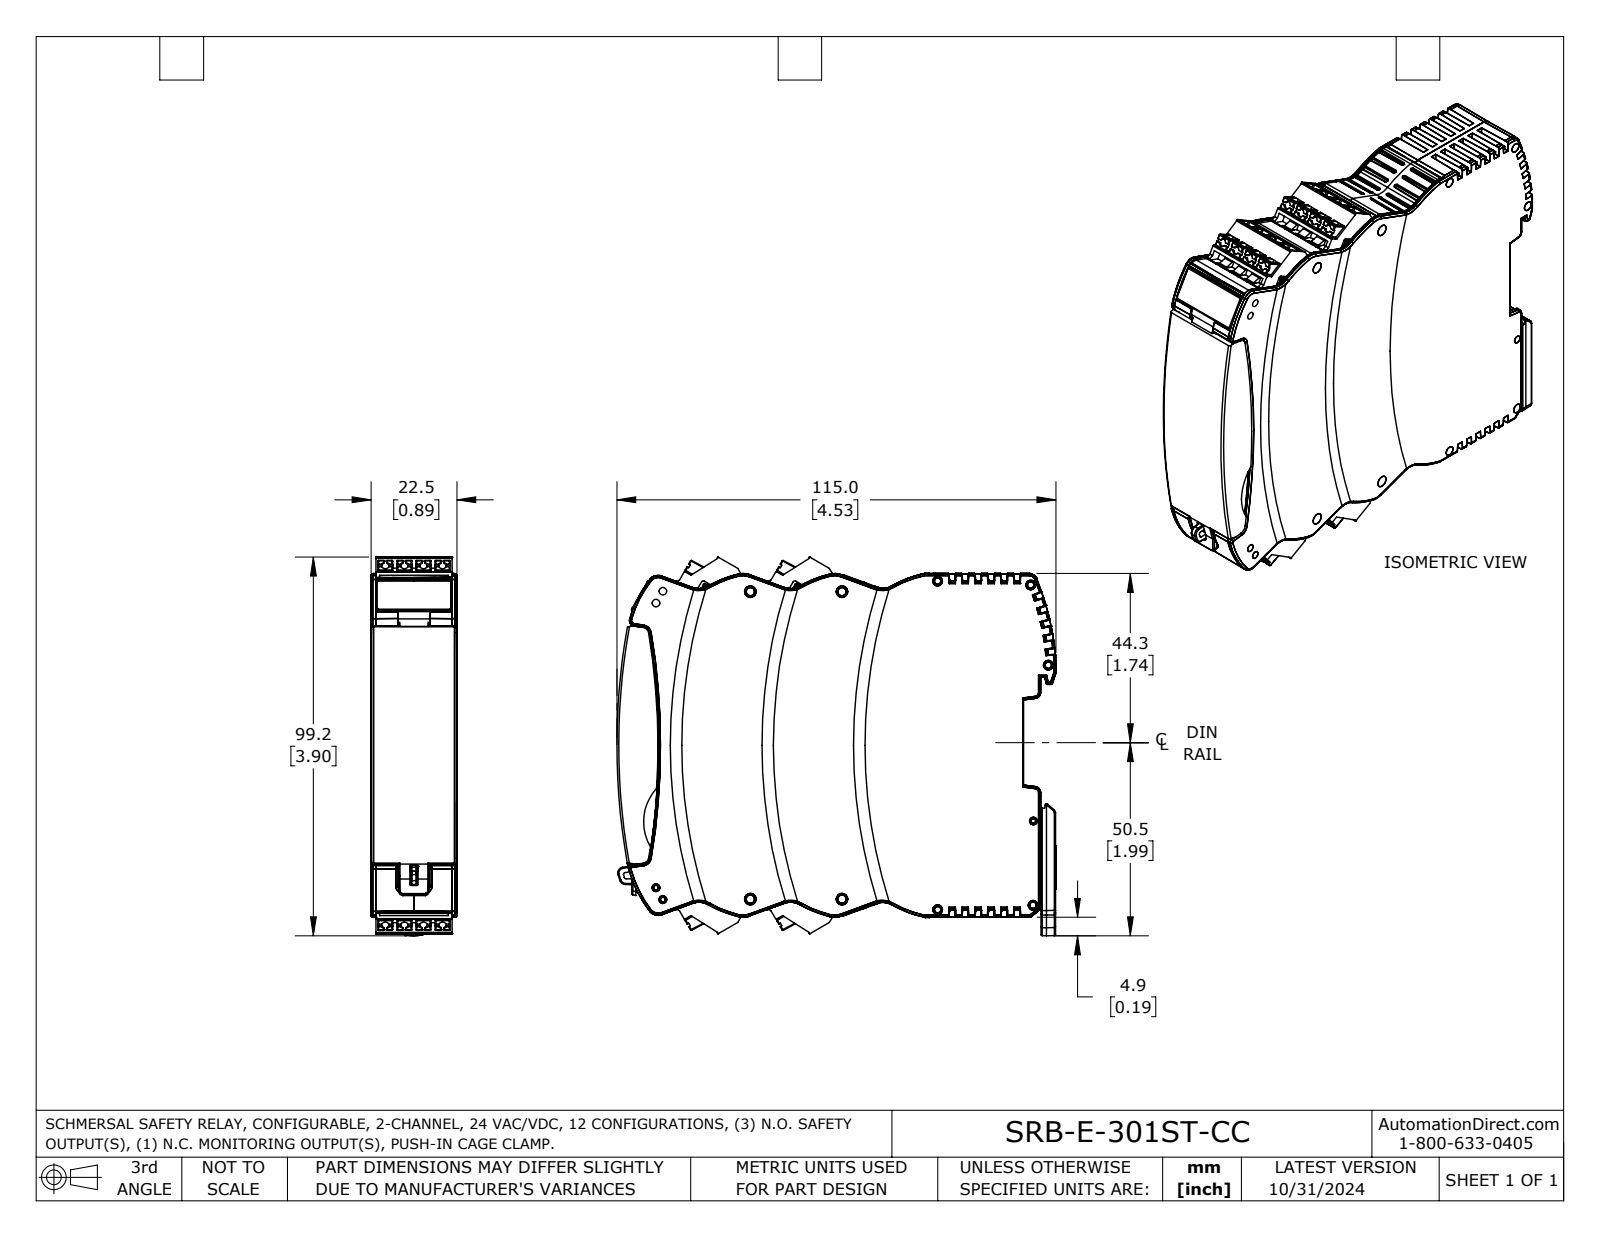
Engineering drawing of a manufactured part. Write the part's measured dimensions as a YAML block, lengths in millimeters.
part_name: "SRB-E-301ST-CC"
step_written_by: "SolidWorks 2023 (AUTOMOTIVE_DESIGN)"
units: millimeters
bodies: {solids: 2, faces: 4347, planar: 2185, cylindrical: 1267, other: 895}
overall_size: [115, 99.2, 22.5]
volume: 211700
surface_area: 43250
round_bosses_or_shafts:
  - {diameter: 1.7, count: 1}
partial_cylinders:
  - {radius: 0.3, count: 233}
  - {radius: 0.2, count: 219}
  - {radius: 0.5, count: 193}
  - {radius: 0.3, count: 60}
  - {radius: 0.1, count: 44}
  - {radius: 1, count: 32}
  - {radius: 1.5, count: 26}
  - {radius: 1.2, count: 16}
face_to_face_distances: [22.5, 3.4, 6.8, 0.9, 4.5, 3.4, 12, 21.6, 20.8, 19.9]
